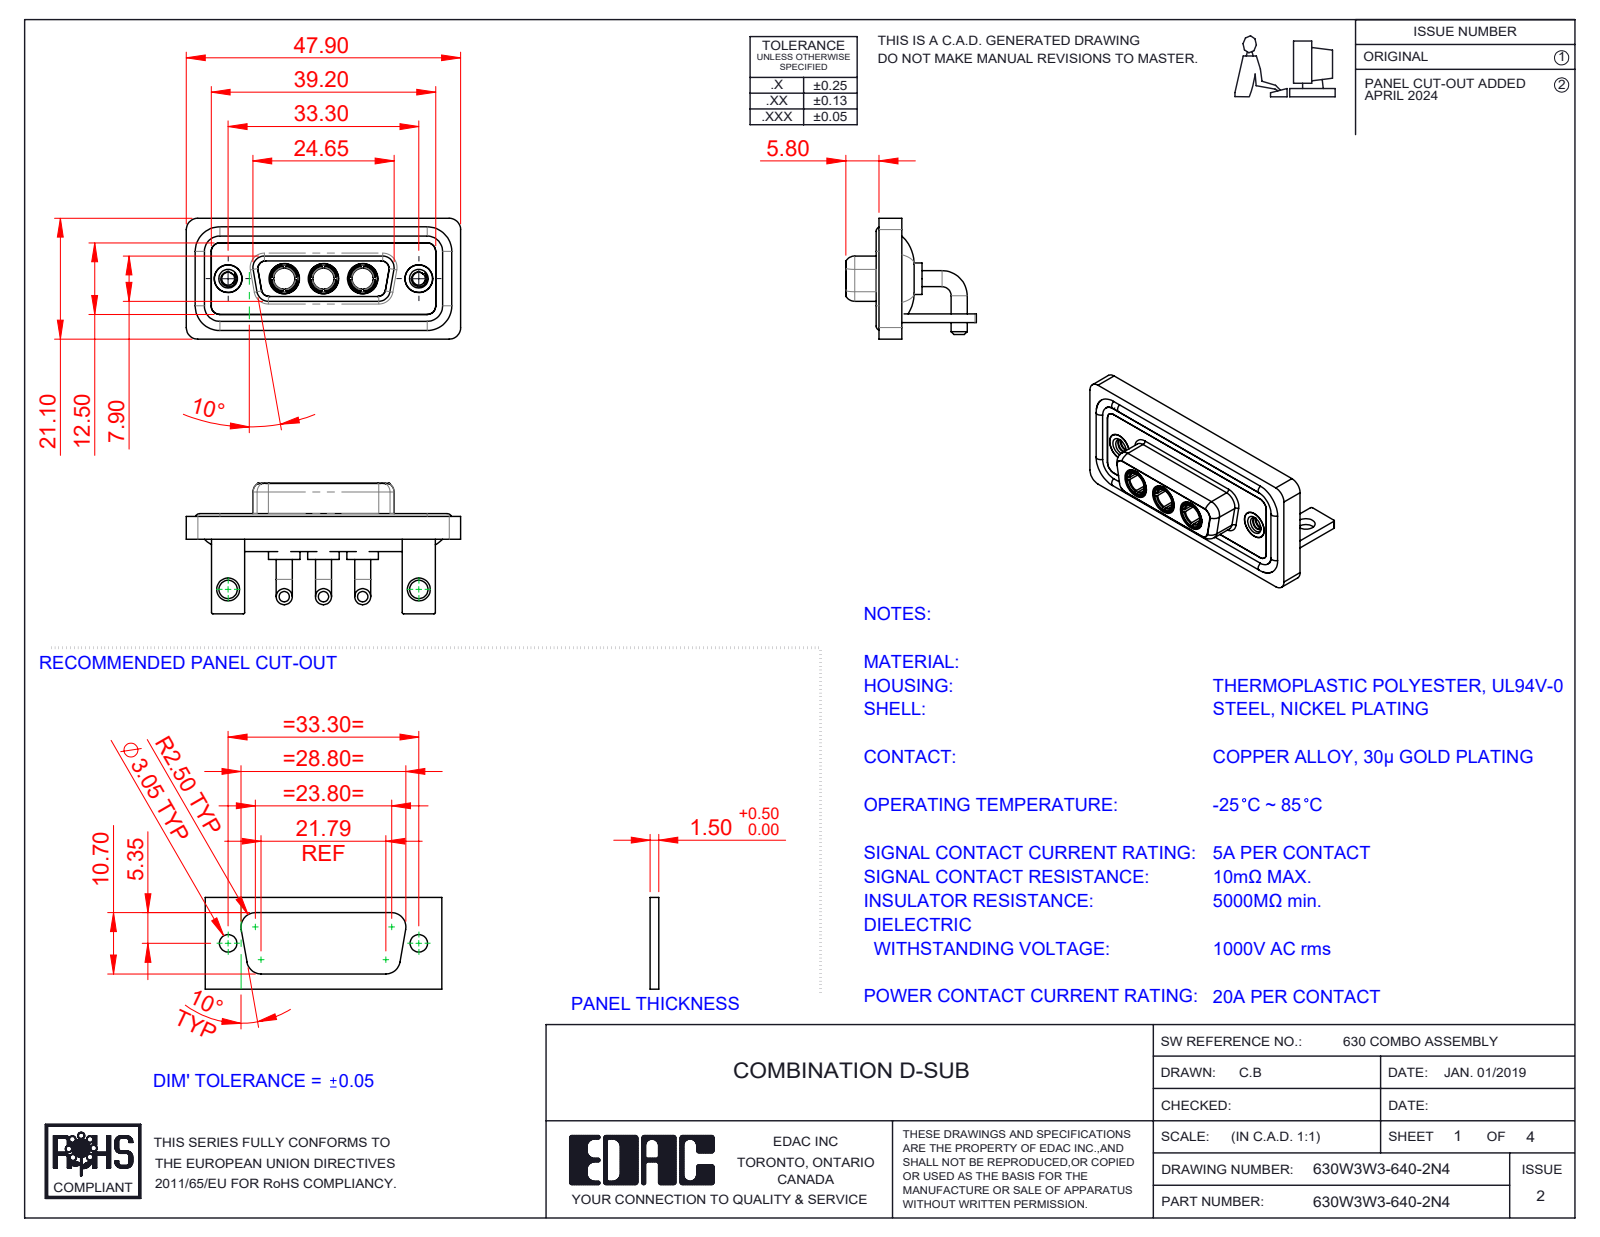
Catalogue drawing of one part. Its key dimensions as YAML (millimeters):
part_name: "630Combo Housing_3W3; 630Combo Stabilizer Bracket_50 Contacts; 630Combo Shell Rear_15 Contacts; 630Combo Waterproof Housing_15 Contacts (+4 more)"
step_written_by: "SolidWorks 2023 (CONFIG_CONTROL_DESIGN)"
units: millimeters
bodies: {solids: 15, faces: 668, planar: 212, cylindrical: 287, other: 169}
overall_size: [47.9, 22.8, 21.1]
volume: 6546
surface_area: 10707
round_holes:
  - {diameter: 4.85, count: 5}
  - {diameter: 3.7, count: 3}
  - {diameter: 5.3, count: 3}
  - {diameter: 2.26, count: 2}
  - {diameter: 3.2, count: 2}
  - {diameter: 4, count: 2}
  - {diameter: 4.05, count: 2}
  - {diameter: 5, count: 2}
round_bosses_or_shafts:
  - {diameter: 2.8, count: 6}
  - {diameter: 1.6, count: 4}
  - {diameter: 5.5, count: 3}
  - {diameter: 5.2, count: 3}
  - {diameter: 4.96, count: 3}
  - {diameter: 4.75, count: 3}
  - {diameter: 3.75, count: 3}
  - {diameter: 4.95, count: 2}
partial_cylinders:
  - {radius: 2, count: 21}
  - {radius: 1.5, count: 18}
  - {radius: 0.25, count: 16}
  - {radius: 1.35, count: 12}
  - {radius: 1.6, count: 8}
  - {radius: 0.5, count: 5}
  - {radius: 0.6, count: 4}
  - {radius: 0.65, count: 4}
face_to_face_distances: [0.4, 2.9, 1.5, 1.8, 3.7, 1.1, 4.1, 1.6, 2.5, 1.4]
hole_center_spacings: [6.85, 9.8, 16.65, 23.5, 33.3, 13.7]
